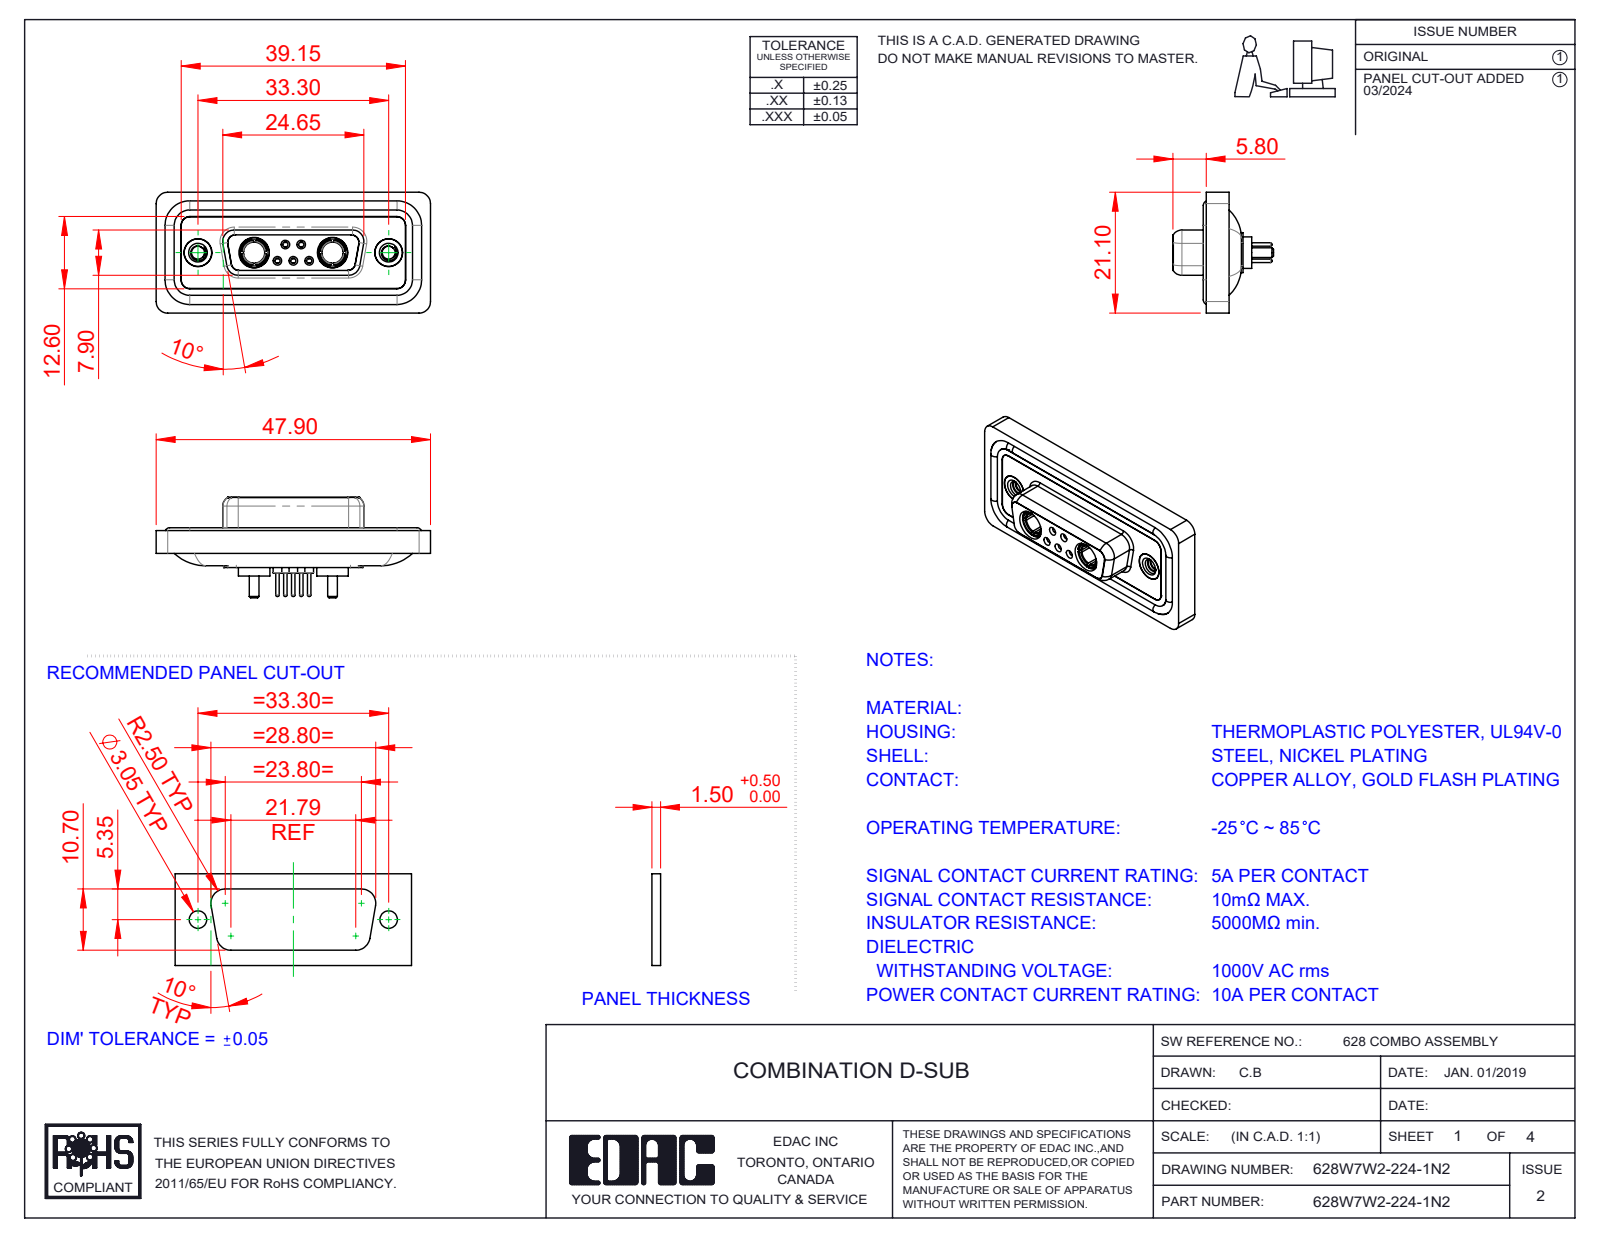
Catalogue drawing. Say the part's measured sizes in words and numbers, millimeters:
The part is named "628Combo Contact Row 1_24; 628Combo Housing_7W2; 628Combo Waterproof Housing_15 Contacts; Power Socket_10A S (+5 more)". Its 3-D file was written by "SolidWorks 2023 (CONFIG_CONTROL_DESIGN)". It is 16 solids with 809 faces: 238 planar, 329 cylindrical and 242 other. Overall it measures 47.9 by 21.1 by 17.55 millimeters. Its volume is 6 048 cubic millimeters and its surface area 9 860 square millimeters. Round holes: 5 of diameter 0.9, 5 of diameter 1.1, 5 of diameter 1.5, 5 of diameter 2, 4 of diameter 4.85, 3 of diameter 1.6, 2 of diameter 1.7, 2 of diameter 2.26, 2 of diameter 3.7, 2 of diameter 4, 2 of diameter 4.05, 2 of diameter 5. Round bosses or shafts: 6 of diameter 1.6, 5 of diameter 2.2, 5 of diameter 0.6, 2 of diameter 5.5, 2 of diameter 5.2, 2 of diameter 4.96, 2 of diameter 4.95, 2 of diameter 4.8. Partial cylindrical surfaces (rounded edges, fillets, slot ends): 22 of radius 1.5, 20 of radius 2, 12 of radius 1.35, 8 of radius 1.6, 4 of radius 0.25, 4 of radius 0.5, 4 of radius 0.6, 4 of radius 0.65. The main face-to-face distances are 0.4, 1.8, 1.6, 0.5, 2.9, 1.1, 7.45, 5.65, 6.6, 7.05. The hole center spacings are 3.16, 2.77, 9.8, 23.5, 4.31, 4.33, 5.03, 5.04.
